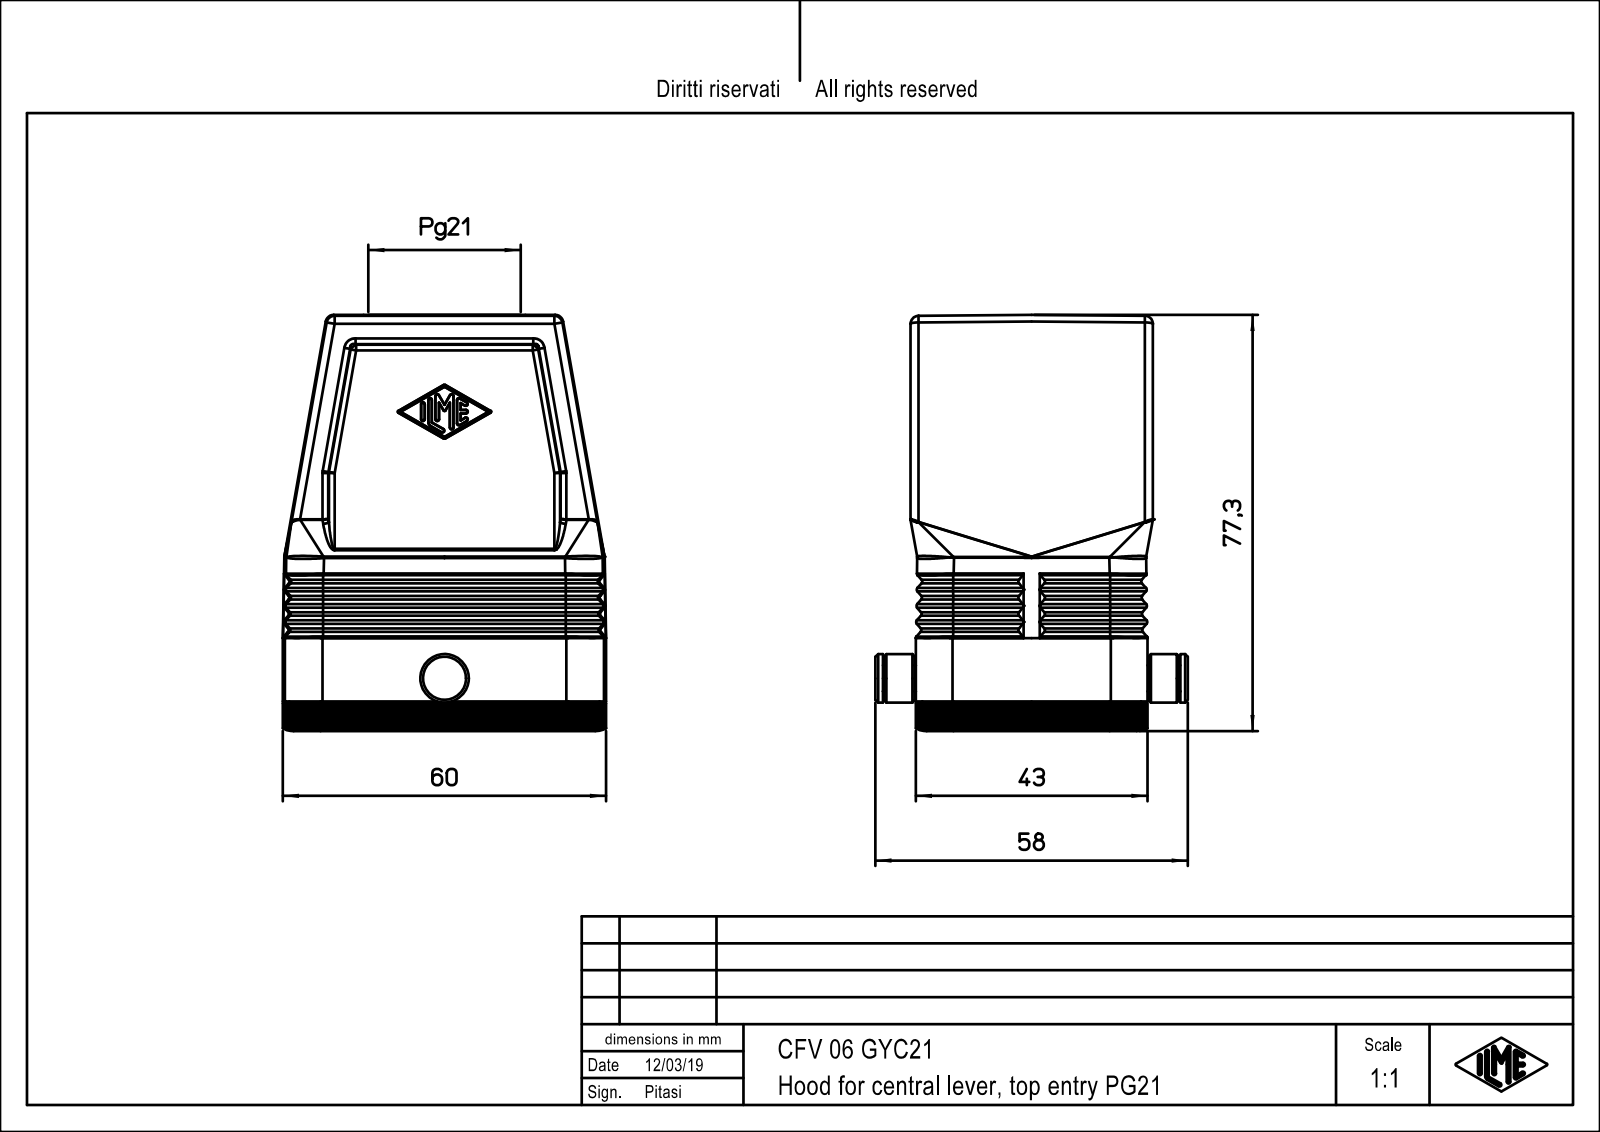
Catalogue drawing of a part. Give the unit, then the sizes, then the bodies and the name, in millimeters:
Units: millimetres
Overall size (bounding box): 77.25 × 60 × 58
Round holes (diameter × count): ⌀3 ×4, ⌀27.54 ×1
Round bosses / shafts (diameter × count): ⌀9 ×1, ⌀4.8 ×1
Partial cylindrical surfaces — rounded edges, fillets, slot ends (radius × count): R0.5 ×54, R1.5 ×44, R3 ×12, R7 ×12, R4 ×4, R4.2 ×4, R5.8 ×4
Main face-to-face distances: 43, 7, 4, 2, 7.55, 1, 44, 60, 39, 66.05
Hole centre spacings: 25.81, 27, 44, 51.62
Volume: 64 731 mm³ · Surface area: 32 033 mm²
Bodies: 1 solid, 515 faces (169 planar, 168 cylindrical, 178 other)
Part name (STEP PRODUCT): CFV_06_GYC21
STEP written by: PTC Creo Elements/Direct Modeling 19.0E 27-Jun-2016 (C) Parametric Technology GmbH (AUTOMOTIVE_DESIGN)
